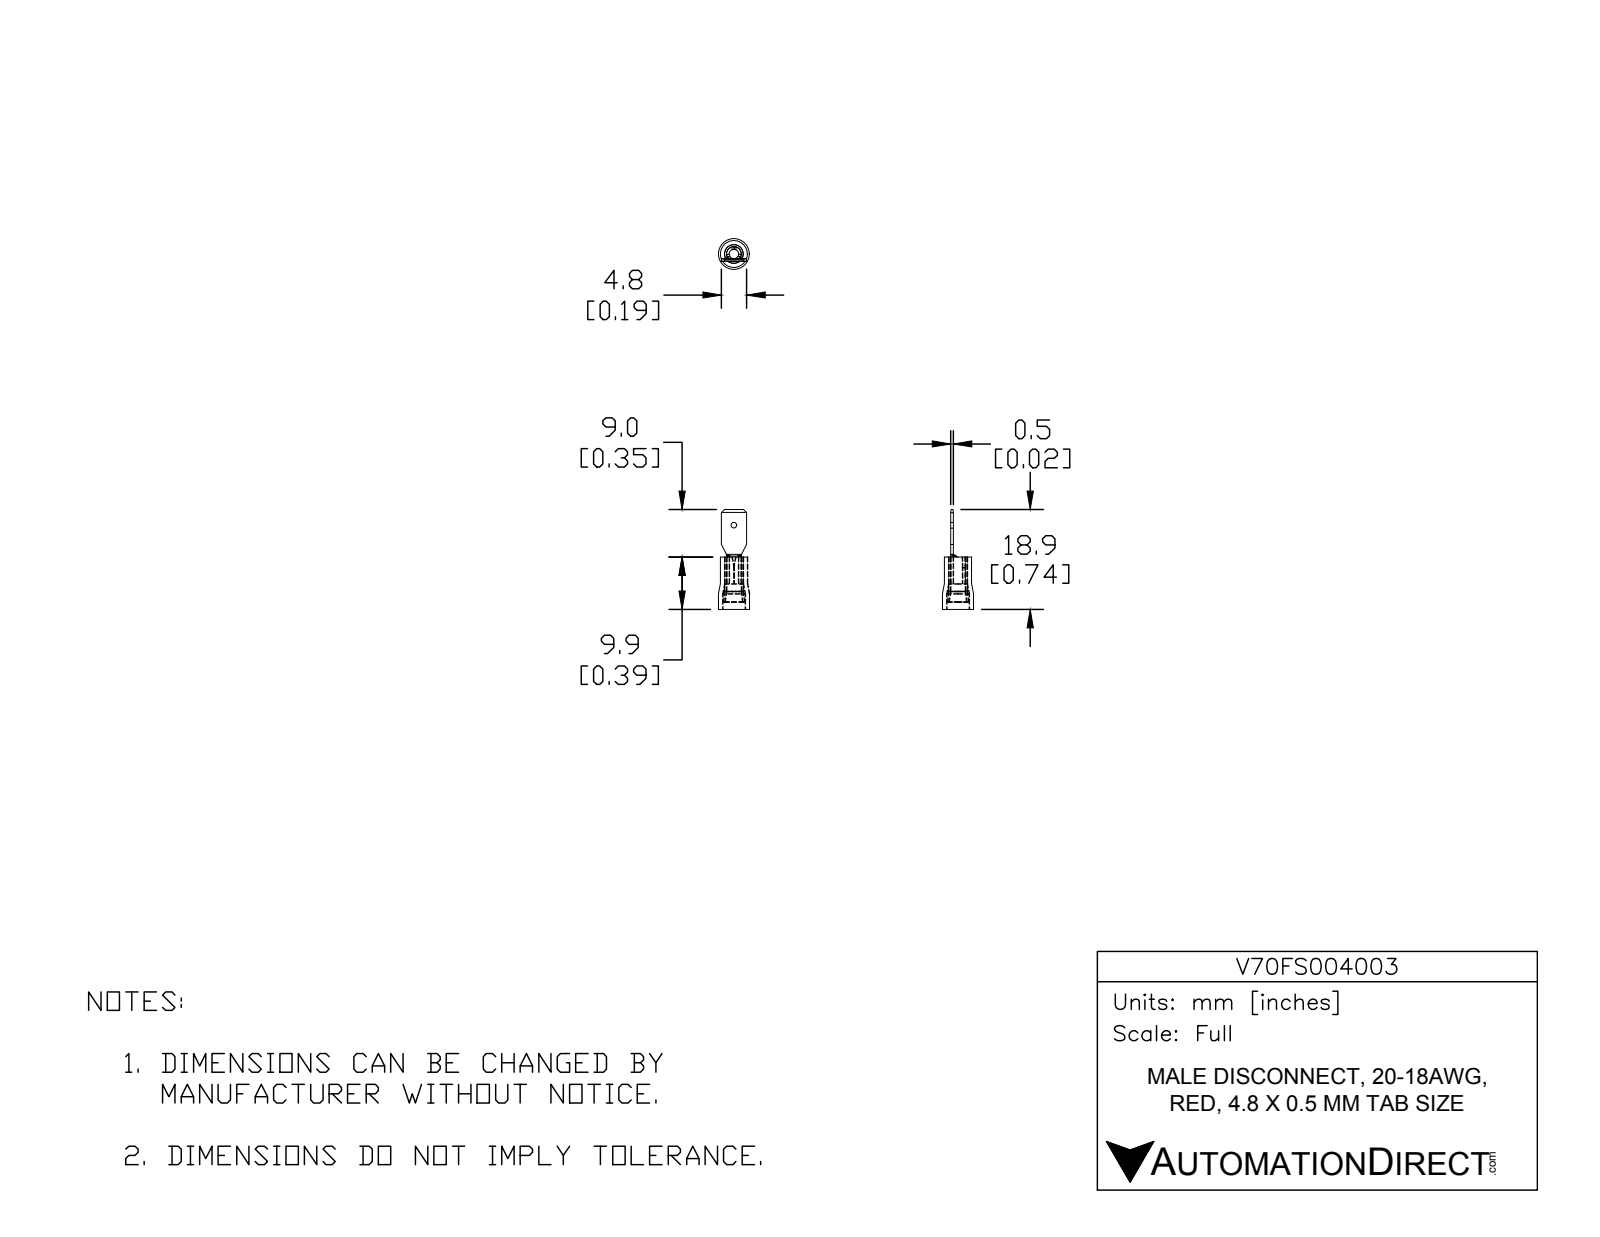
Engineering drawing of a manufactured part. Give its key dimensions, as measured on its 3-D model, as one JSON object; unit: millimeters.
{"part_name": "V70FS004003", "step_written_by": "SolidWorks 2017 (AUTOMOTIVE_DESIGN)", "units": "millimeters", "bodies": {"solids": 3, "faces": 59, "planar": 19, "cylindrical": 22, "other": 18}, "overall_size": [18.9, 5.87, 5.87], "volume_mm3": 182, "surface_area_mm2": 663, "round_holes": [[1.1, 1], [1.76, 1], [2.8, 1], [3.53, 1], [4.27, 1]], "round_bosses_or_shafts": [[5.87, 1], [5.13, 1], [3.5, 1], [2.76, 1]], "partial_cylinders_radius": [[5.89, 2]], "face_to_face_distances": [0.5, 9.9, 4.9, 5, 2.37, 2.43, 4.8, 18.9, 14, 9]}
